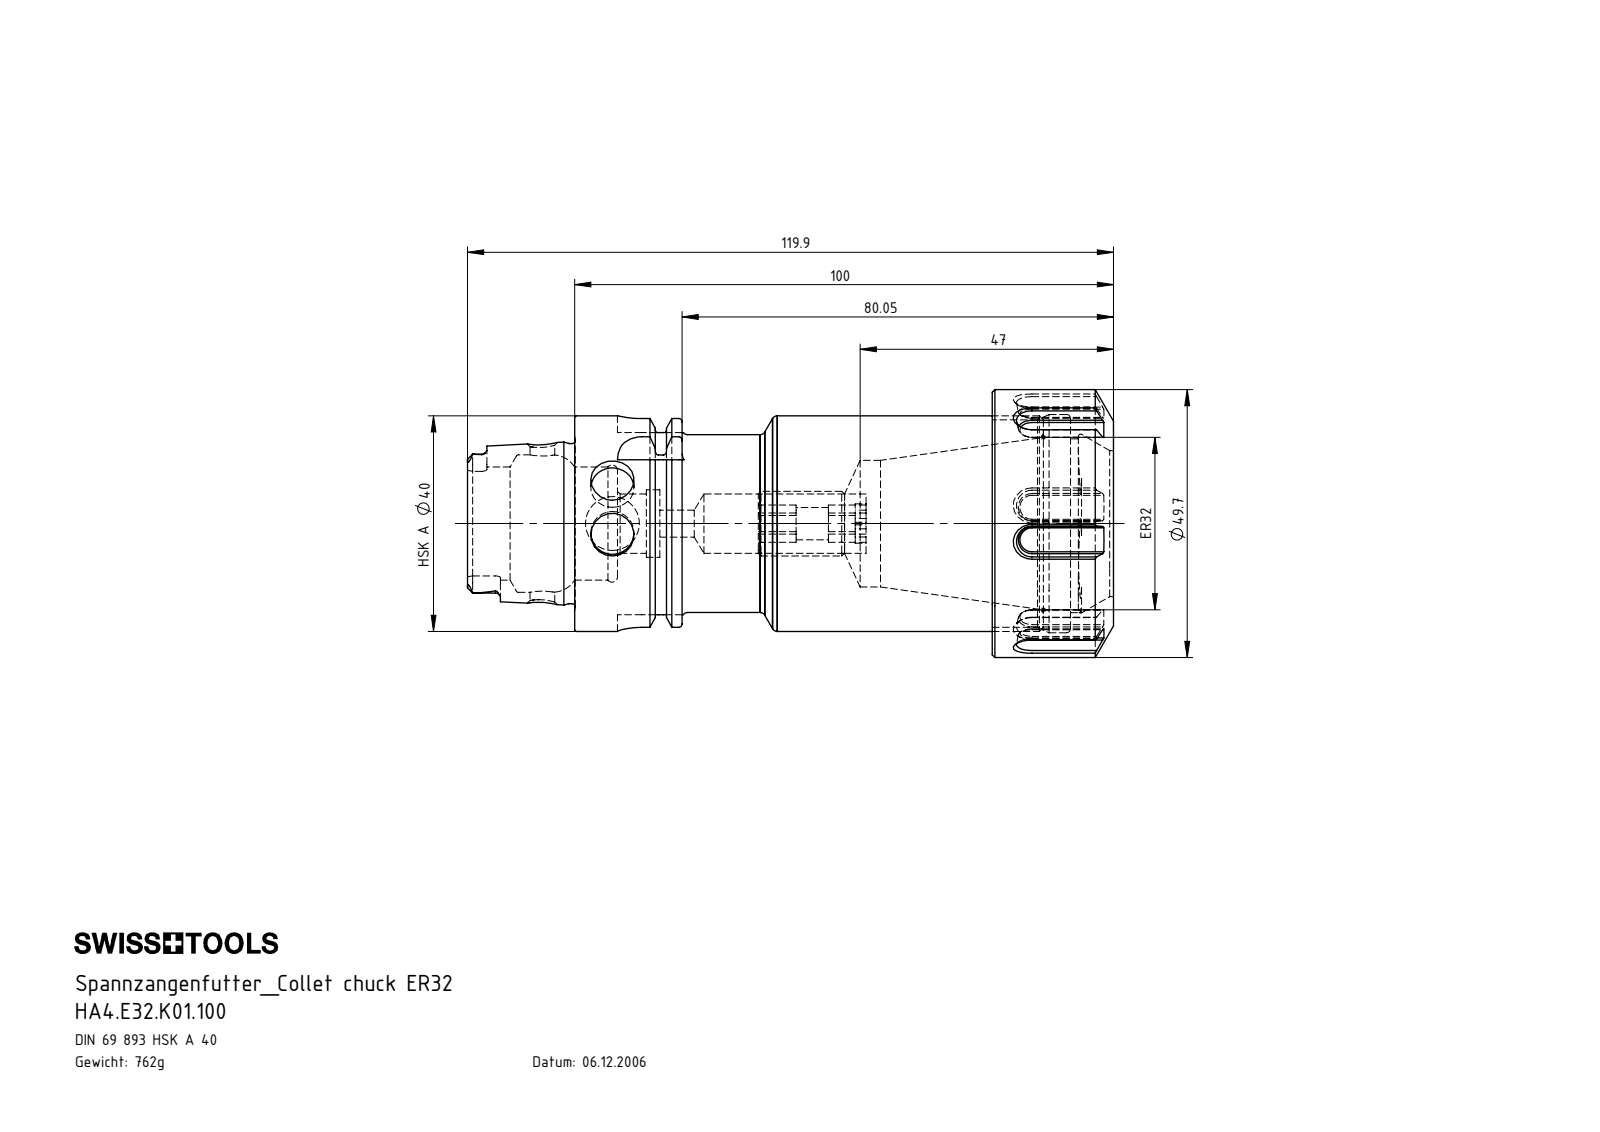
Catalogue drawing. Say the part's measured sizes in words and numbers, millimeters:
The part is named "HA4.E32.K01.100; E32-ER1.001.022; ERU-AN5.K01.020_A; HA4-E32.K01.100_B_Fertigbearbeitung". Its 3-D file was written by "SolidWorks 2017 (CONFIG_CONTROL_DESIGN)". It is 3 solids with 323 faces: 132 planar, 73 cylindrical and 118 other. Overall it measures 119.9 by 49.7 by 49.7 millimeters. Its volume is 97 109 cubic millimeters and its surface area 31 763 square millimeters. Round holes: 2 of diameter 8, 1 of diameter 4.6, 1 of diameter 5, 1 of diameter 6, 1 of diameter 10, 1 of diameter 11, 1 of diameter 12.5, 1 of diameter 21, 1 of diameter 23.5, 1 of diameter 25.5, 1 of diameter 27.1, 1 of diameter 38.5. Round bosses or shafts: 1 of diameter 49.7, 1 of diameter 40, 1 of diameter 34.75, 1 of diameter 33, 1 of diameter 29.71, 1 of diameter 12. Partial cylindrical surfaces (rounded edges, fillets, slot ends): 6 of radius 0.9, 4 of radius 1.88, 4 of radius 4.5, 2 of radius 15.5. The main face-to-face distances are 7.95, 92.05, 22.5, 77.5, 100, 14.55, 5.05, 13, 87, 9.5.
